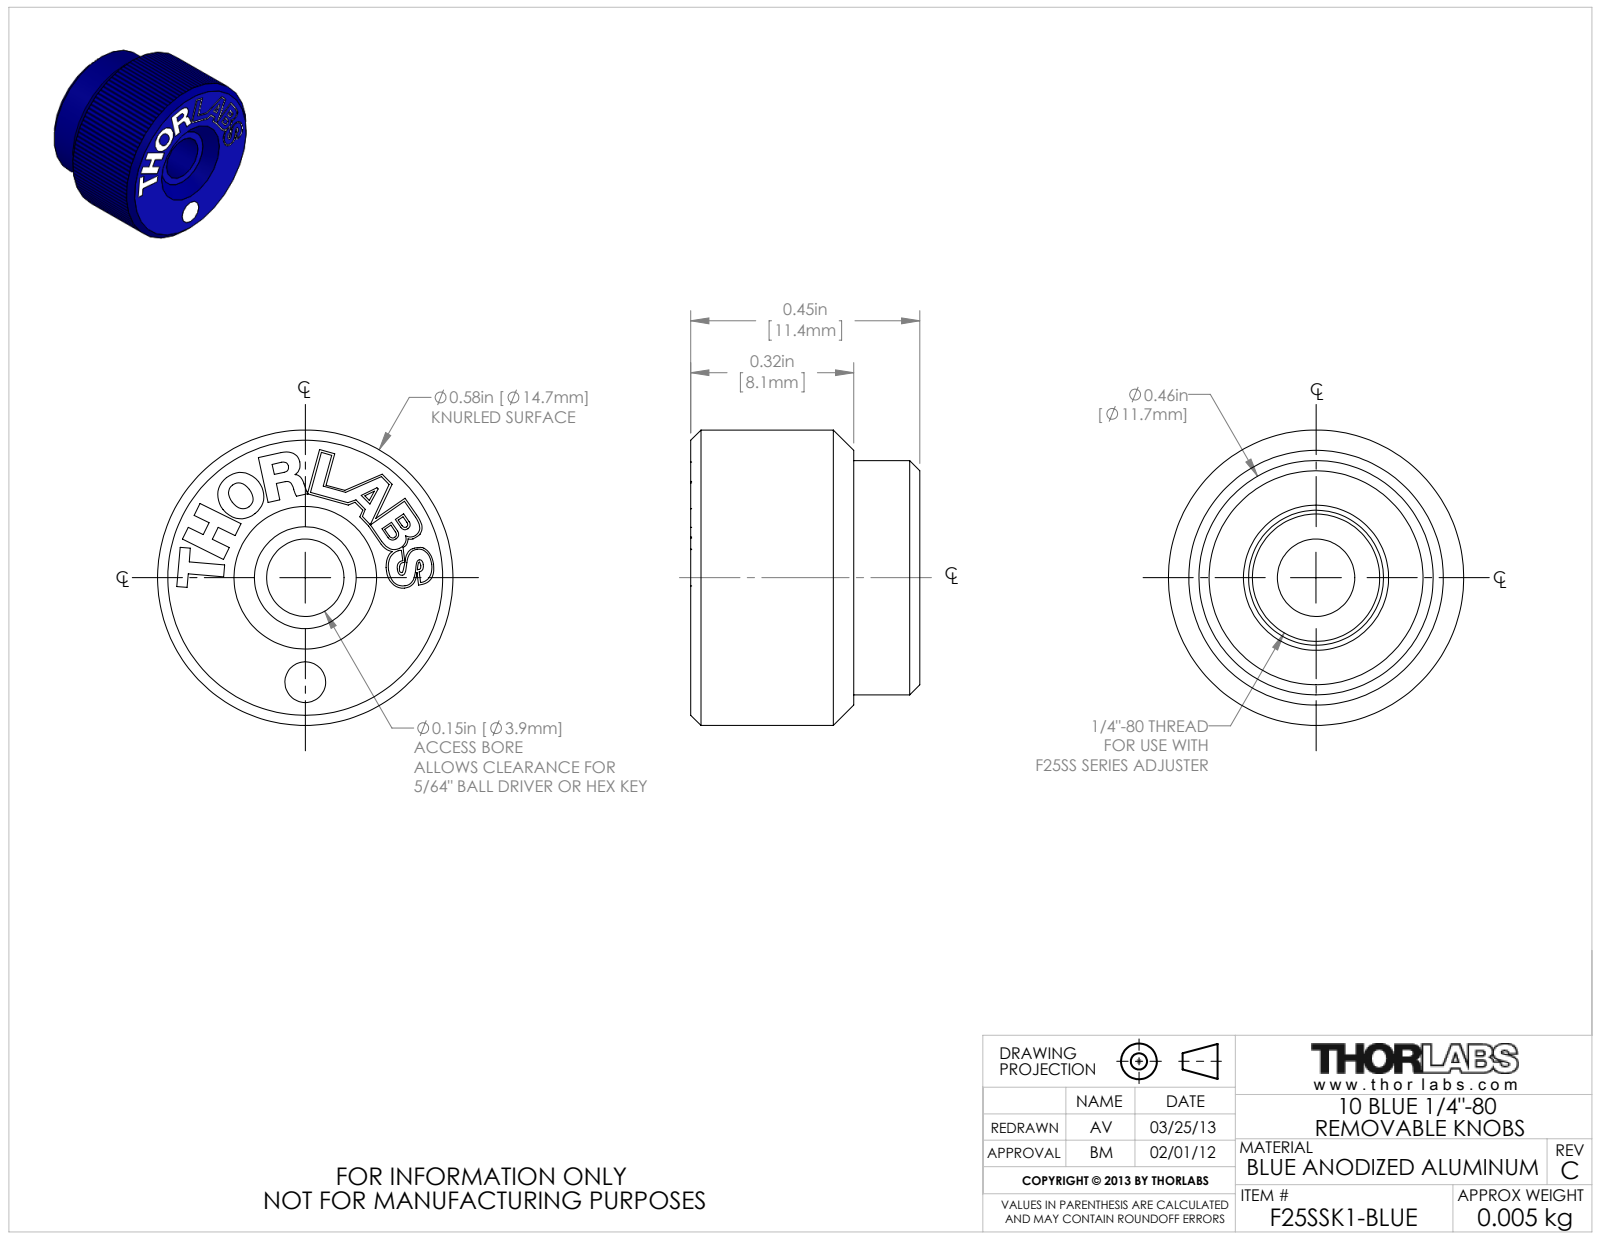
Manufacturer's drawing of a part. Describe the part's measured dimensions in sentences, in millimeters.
The part is named "23388-E0W". Its 3-D file was written by "SolidWorks 2012 (AUTOMOTIVE_DESIGN)". It is 1 solid with 210 faces: 118 planar, 21 cylindrical and 71 other. Overall it measures 14.7 by 14.7 by 11.4 millimeters. Its volume is 1 400 cubic millimeters and its surface area 953 square millimeters. Round holes: 1 of diameter 2, 1 of diameter 3.9, 1 of diameter 6.4, 1 of diameter 6.7, 1 of diameter 7.4. Round bosses or shafts: 1 of diameter 14.7, 1 of diameter 11.7. Partial cylindrical surfaces (rounded edges, fillets, slot ends): 1 of radius 0.4, 1 of radius 1.2, 1 of radius 1.5. The main face-to-face distances are 11.4, 6.9, 4.6, 8.1, 1.3, 3.3, 6.9, 8.1, 11.4, 0.5. The hole center spacings are 5.2.
